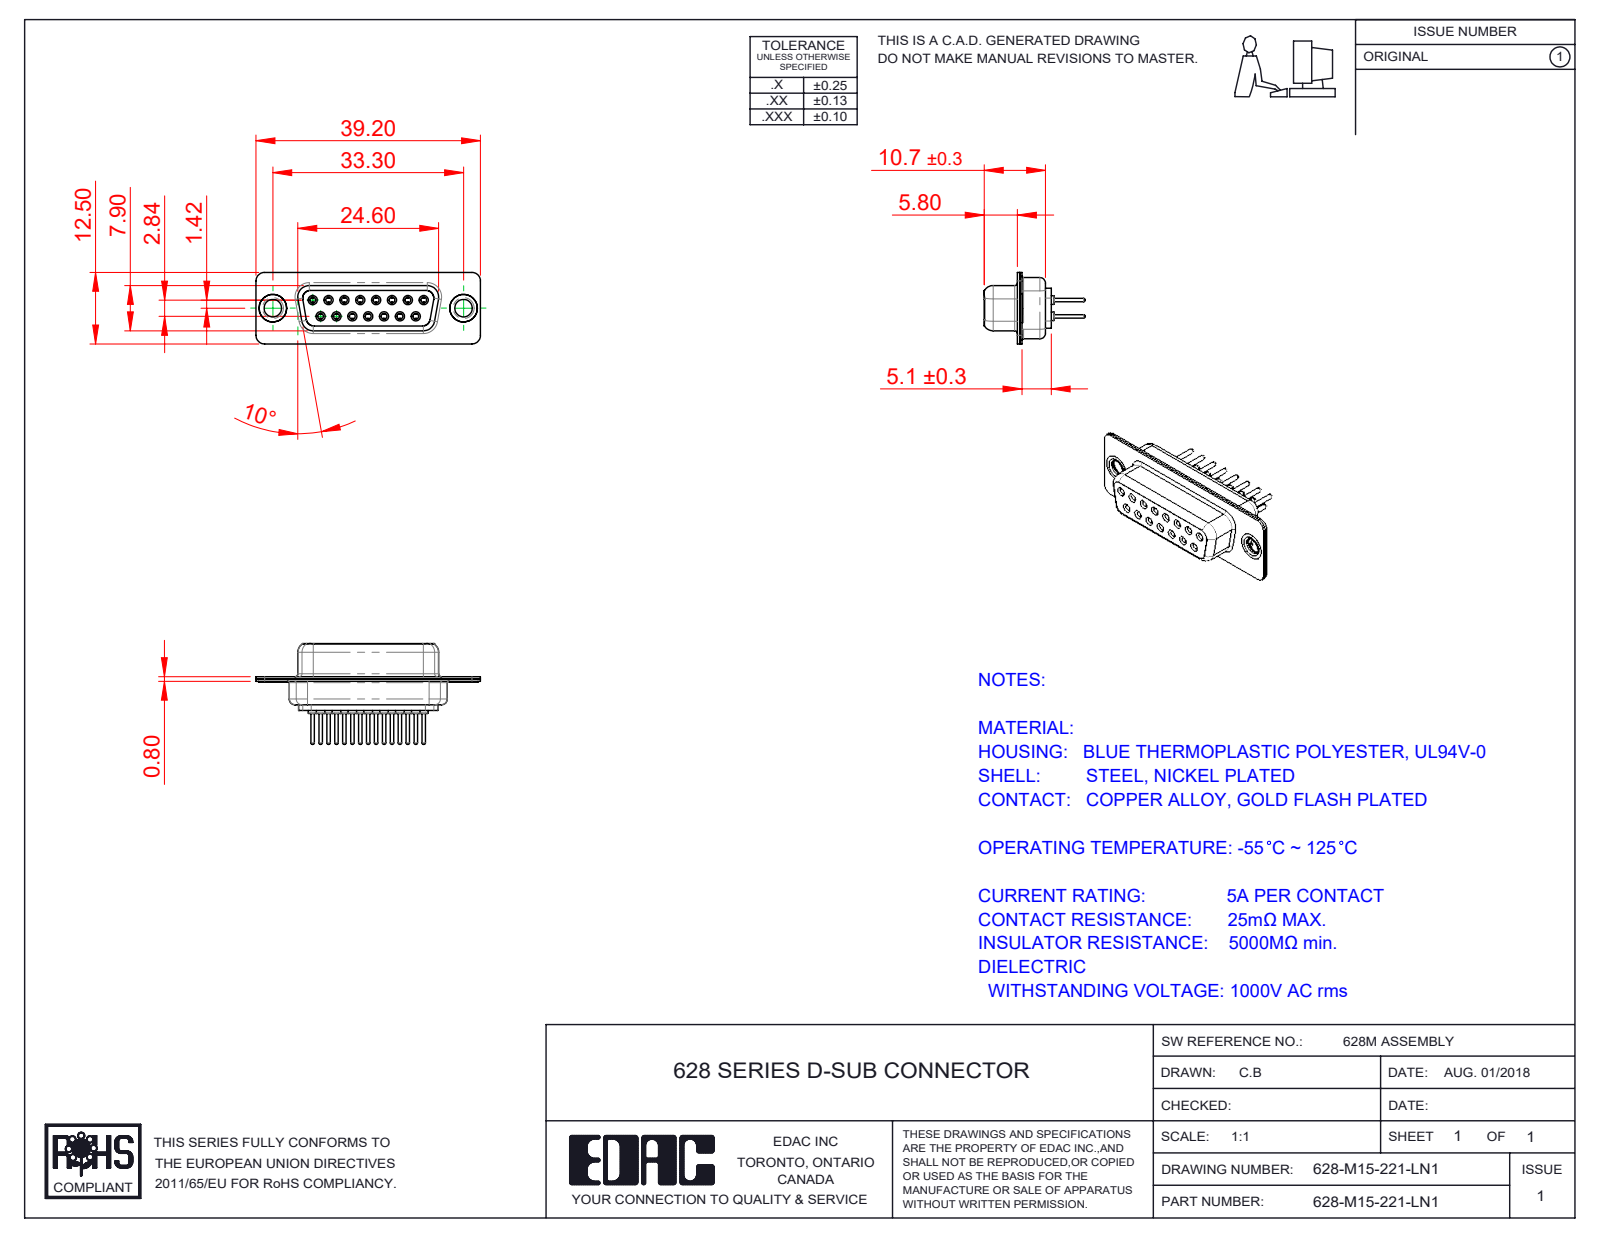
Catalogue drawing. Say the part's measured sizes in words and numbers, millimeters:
The part is named "628M Thru Hole Rivet; 628M Contact Row 1_21; 628-M15-221-LN1; 628M Contact Row 2_21 (+3 more)". Its 3-D file was written by "SolidWorks 2020 (CONFIG_CONTROL_DESIGN)". It is 20 solids with 1078 faces: 292 planar, 406 cylindrical and 380 other. Overall it measures 39.2 by 17.6 by 12.5 millimeters. Its volume is 2 393 cubic millimeters and its surface area 6 054 square millimeters. Round holes: 15 of diameter 1, 15 of diameter 1.1, 15 of diameter 1.7, 15 of diameter 1.8, 15 of diameter 2, 2 of diameter 3.05, 2 of diameter 4, 2 of diameter 4.8. Round bosses or shafts: 15 of diameter 2.2, 15 of diameter 1.6, 15 of diameter 1.5, 15 of diameter 0.6, 2 of diameter 5, 2 of diameter 4.9, 2 of diameter 3.55. Partial cylindrical surfaces (rounded edges, fillets, slot ends): 16 of radius 1.5, 12 of radius 2, 8 of radius 1.35, 8 of radius 1.6, 4 of radius 0.25, 4 of radius 0.5, 4 of radius 0.6, 4 of radius 0.65. The main face-to-face distances are 0.4, 1.4, 0.45, 8.45, 8.9, 1.8, 6.2, 7.05, 1, 1.35. The hole center spacings are 3.16, 2.77, 5.54, 8.31, 11.08, 5.03, 5.04, 7.48.
